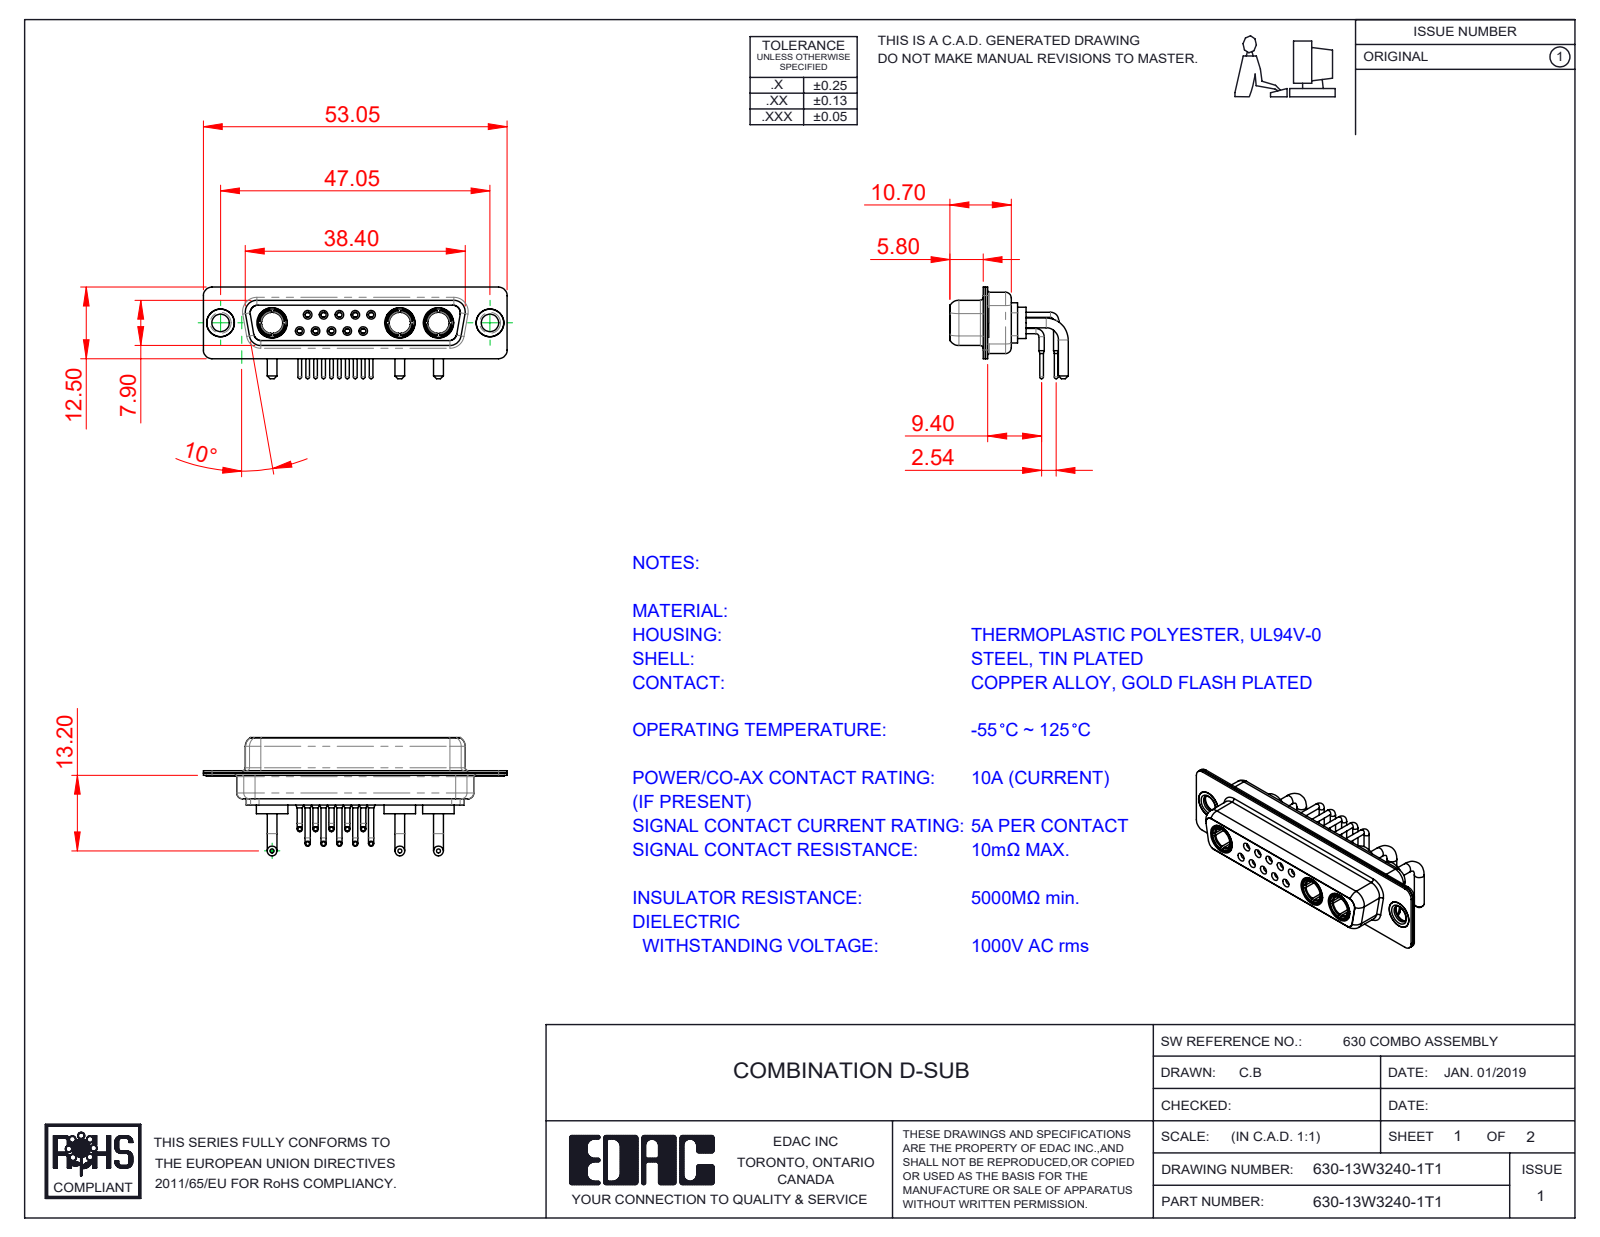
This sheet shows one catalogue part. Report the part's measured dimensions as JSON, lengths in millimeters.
{"part_name": "630Combo Housing_13W3; 630Combo Contact Row 1; 630Combo Contact Row 2; 630Combo Thru Hole Rivet (+4 more)", "step_written_by": "SolidWorks 2020 (CONFIG_CONTROL_DESIGN)", "units": "millimeters", "bodies": {"solids": 21, "faces": 1017, "planar": 304, "cylindrical": 426, "other": 287}, "overall_size": [53.05, 20.65, 16], "volume_mm3": 3775, "surface_area_mm2": 8721, "round_holes": [[0.9, 10], [1.1, 10], [1.5, 10], [2, 10], [1.6, 5], [1.7, 5], [4.85, 5], [3.7, 3], [5.3, 3], [3.05, 2], [4, 2], [4.05, 2]], "round_bosses_or_shafts": [[0.9, 10], [0.65, 10], [1.7, 6], [1.6, 5], [5.5, 3], [5.2, 3], [4.96, 3], [4.75, 3]], "partial_cylinders_radius": [[1.5, 16], [2, 12], [1.35, 8], [1.6, 8], [0.25, 4], [0.5, 4], [0.6, 4], [0.65, 4]], "face_to_face_distances": [0.4, 0.45, 1.4, 8.45, 8.9, 1.8, 6.2, 7.05, 7.5, 1.85], "hole_center_spacings": [3.16, 2.77, 5.54, 5.03, 5.04, 8.31, 7.48, 7.49]}
